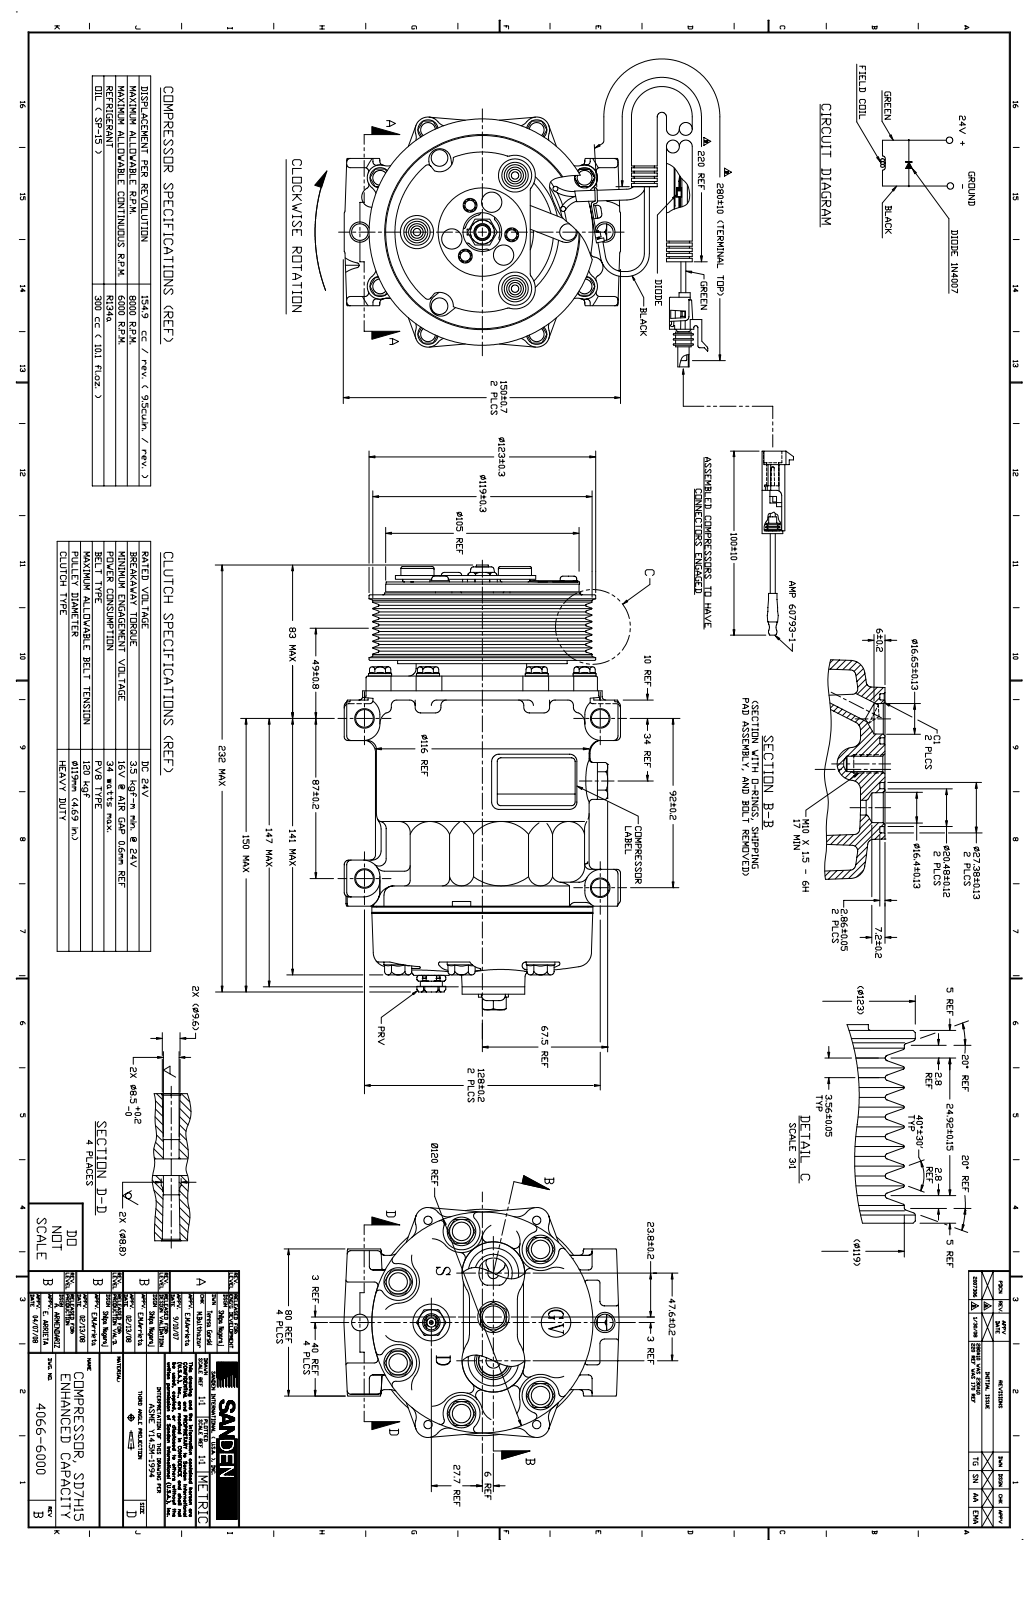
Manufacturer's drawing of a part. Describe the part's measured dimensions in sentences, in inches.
The part is named "SANDEN_4066_REV_B_COMPR_AC". Its 3-D file was written by "SolidWorks 2007 (CONFIG_CONTROL_DESIGN)". It is 1 solid with 2894 faces: 695 planar, 699 cylindrical and 1500 other. Overall it measures 19.718 by 9.021 by 4.921 inches. Its volume is 138.3 cubic inches and its surface area 413.9 square inches. Round holes: 13 of diameter 0.335, 7 of diameter 0.315, 6 of diameter 0.469, 3 of diameter 0.201, 3 of diameter 0.25, 3 of diameter 0.295, 2 of diameter 0.354, 2 of diameter 1.078, 1 of diameter 0.138, 1 of diameter 0.157, 1 of diameter 0.264, 1 of diameter 0.394. Round bosses or shafts: 8 of diameter 0.508, 6 of diameter 0.602, 6 of diameter 0.106, 4 of diameter 0.63, 3 of diameter 0.709, 3 of diameter 0.433, 3 of diameter 0.354, 3 of diameter 0.197. Partial cylindrical surfaces (rounded edges, fillets, slot ends): 38 of radius 0.02, 37 of radius 0.079, 32 of radius 0.276, 26 of radius 0.118, 24 of radius 0.059, 20 of radius 0.098, 17 of radius 0.197, 15 of radius 0.394. The main face-to-face distances are 0.079, 1.769, 0.165, 1.765, 1.958, 0.189, 0.024, 1.793, 0.252, 1.517. The hole center spacings are 2.474, 3.5, 1.657, 0.63, 1.239, 1.448, 2.323, 2.626.
